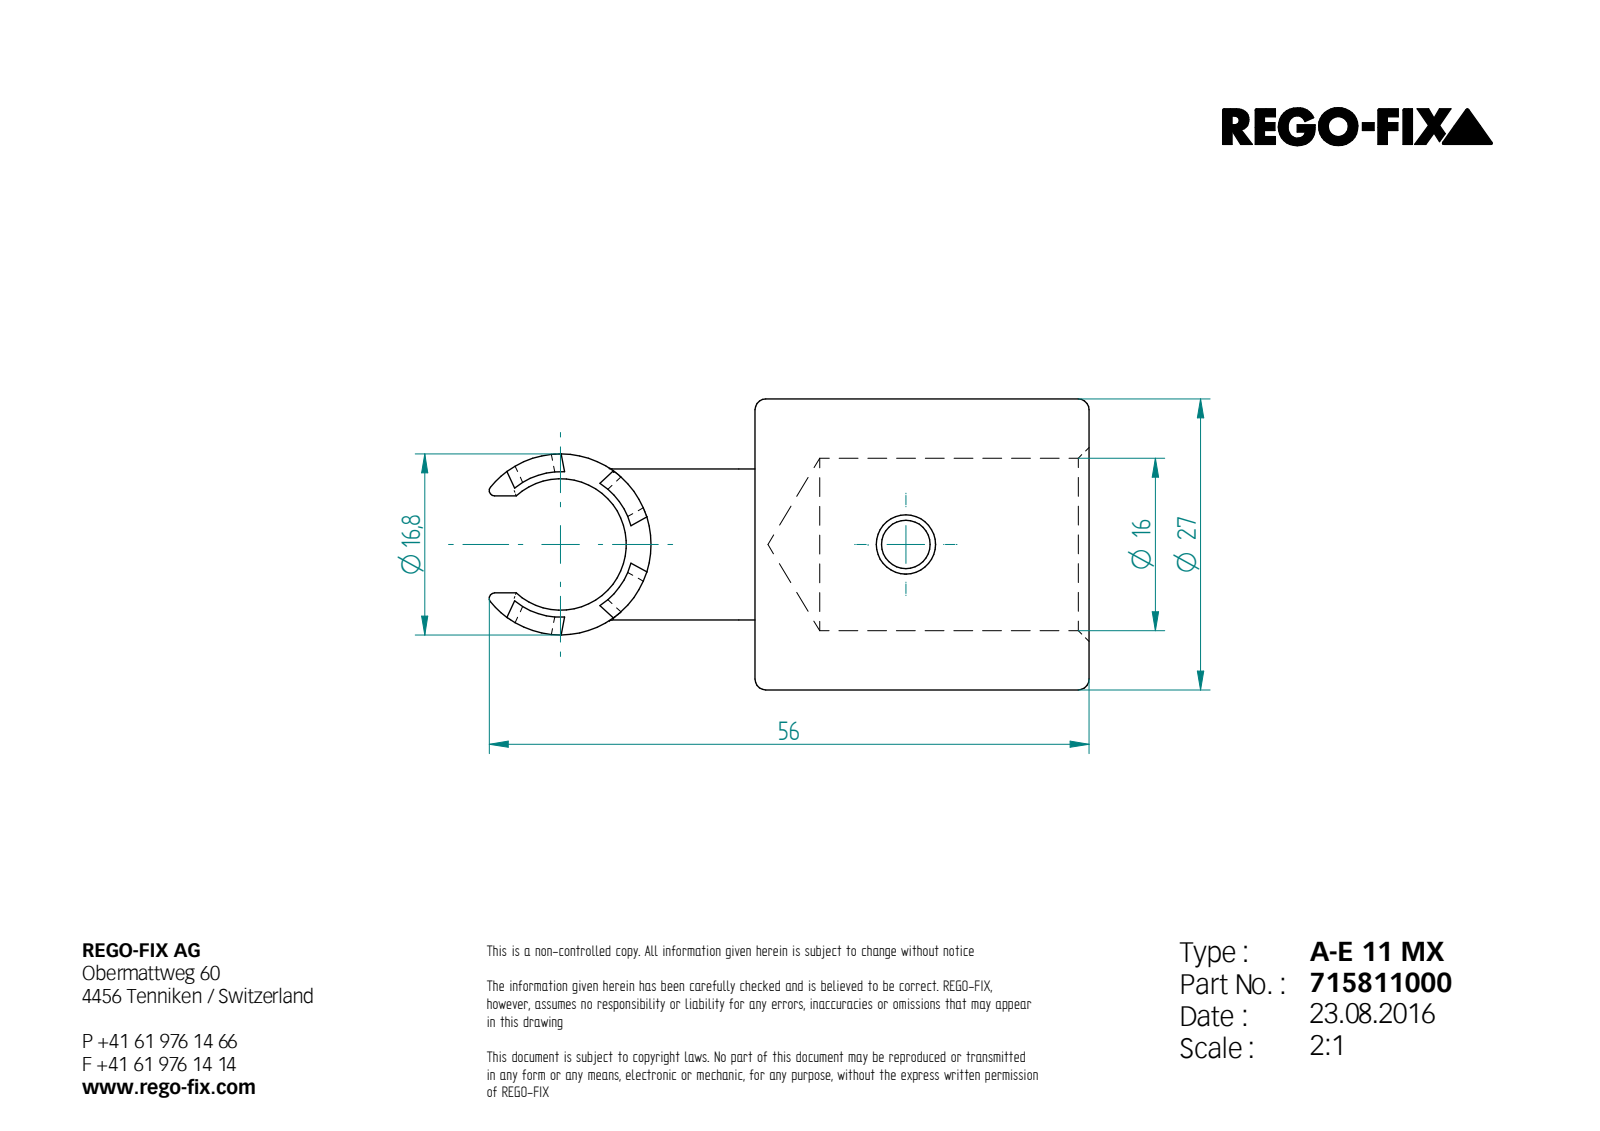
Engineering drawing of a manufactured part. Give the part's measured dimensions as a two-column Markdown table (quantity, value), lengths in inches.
| quantity | value |
| --- | --- |
| STEP written by | Unknown (AUTOMOTIVE_DESIGN) |
| units | inches |
| bodies | 1 solid, 70 faces (23 planar, 28 cylindrical, 19 other) |
| overall size | 2.192 × 1.063 × 1.063 |
| volume | 0.798 in³ |
| surface area | 9.382 in² |
| round holes (diameter × count) | 0.177 × 1, 0.217 × 1, 0.63 × 1 |
| round bosses / shafts (diameter × count) | 1.063 × 1 |
| partial cylindrical surfaces (radius × count) | 0.035 × 8, 0.02 × 4, 0.059 × 2, 0.079 × 2, 0.157 × 1, 0.24 × 1, 0.266 × 1, 0.331 × 1 |
| main face-to-face distances | 1.22, 0.157, 0.063, 0.22, 0.354, 0.134, 0.197, 0.02, 0.335, 0.098 |
